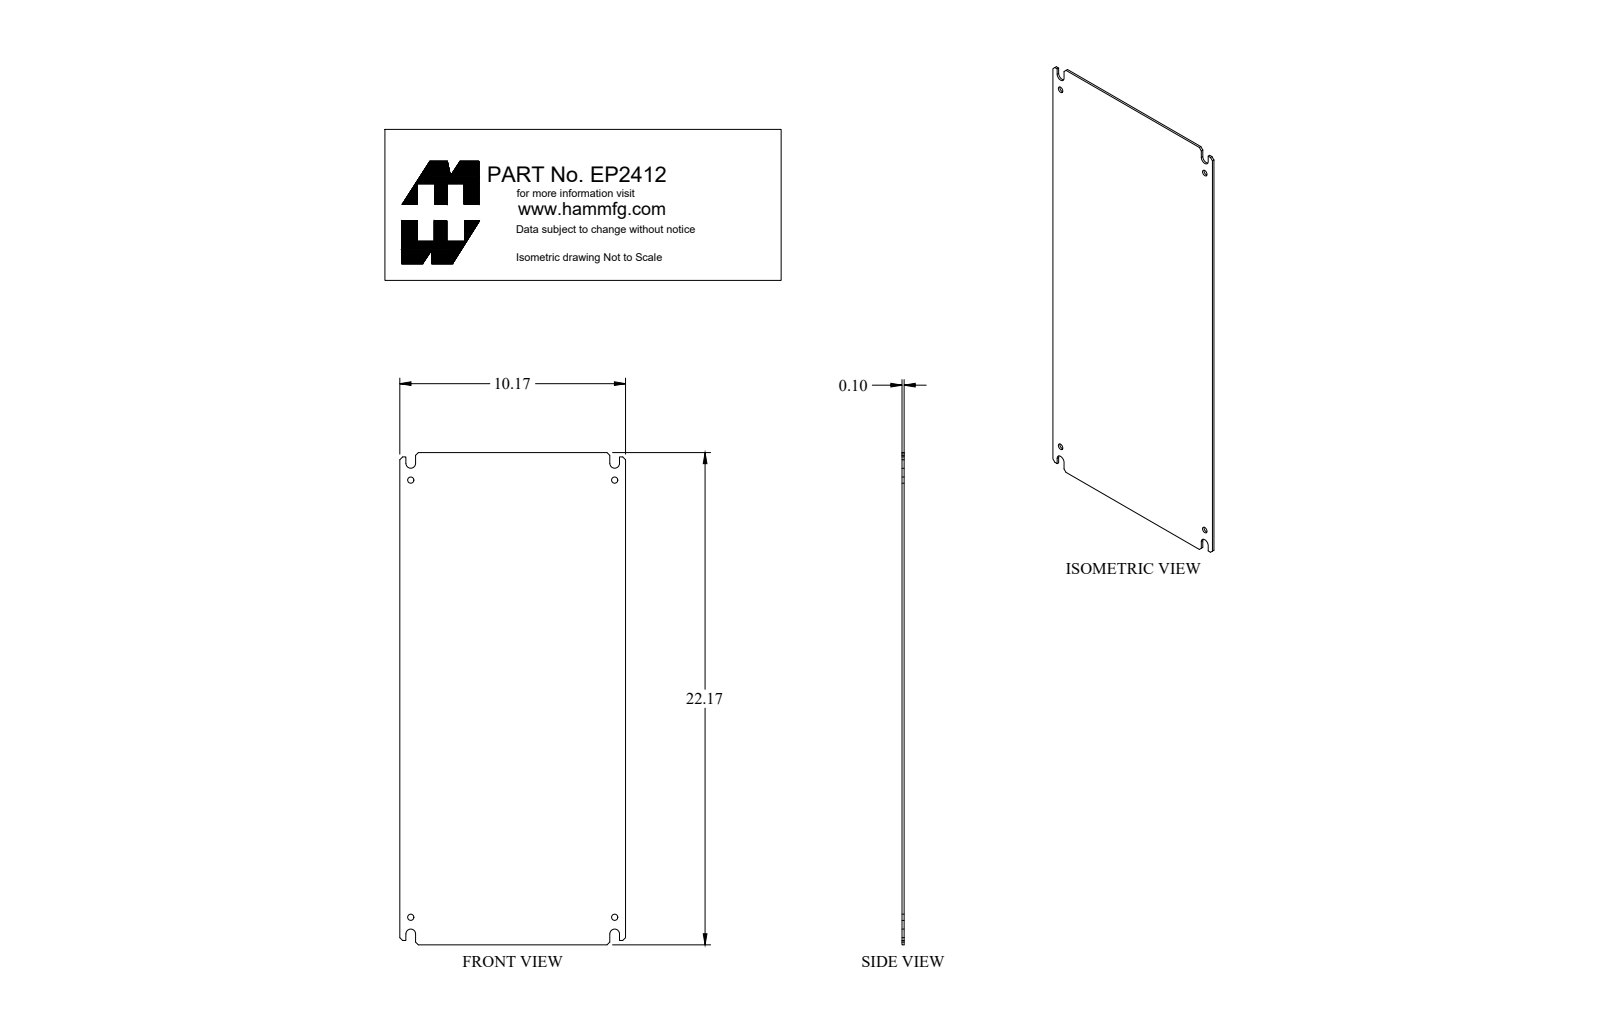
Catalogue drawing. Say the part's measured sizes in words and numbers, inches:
The part is named "EP2412". Its 3-D file was written by "SolidWorks 2018 (AUTOMOTIVE_DESIGN)". It is 1 solid with 40 faces: 26 planar, 14 cylindrical and 0 other. Overall it measures 22.17 by 10.17 by 0.095 inches. Its volume is 21.26 cubic inches and its surface area 454.3 square inches. Round holes: 4 of diameter 0.281. Partial cylindrical surfaces (rounded edges, fillets, slot ends): 4 of radius 0.219. The main face-to-face distances are 0.095, 10.17, 22.17, 0.709, 9.461, 0.272, 9.898, 0.437, 9.188, 8.751. The hole center spacings are 9.188, 19.688, 21.727.
